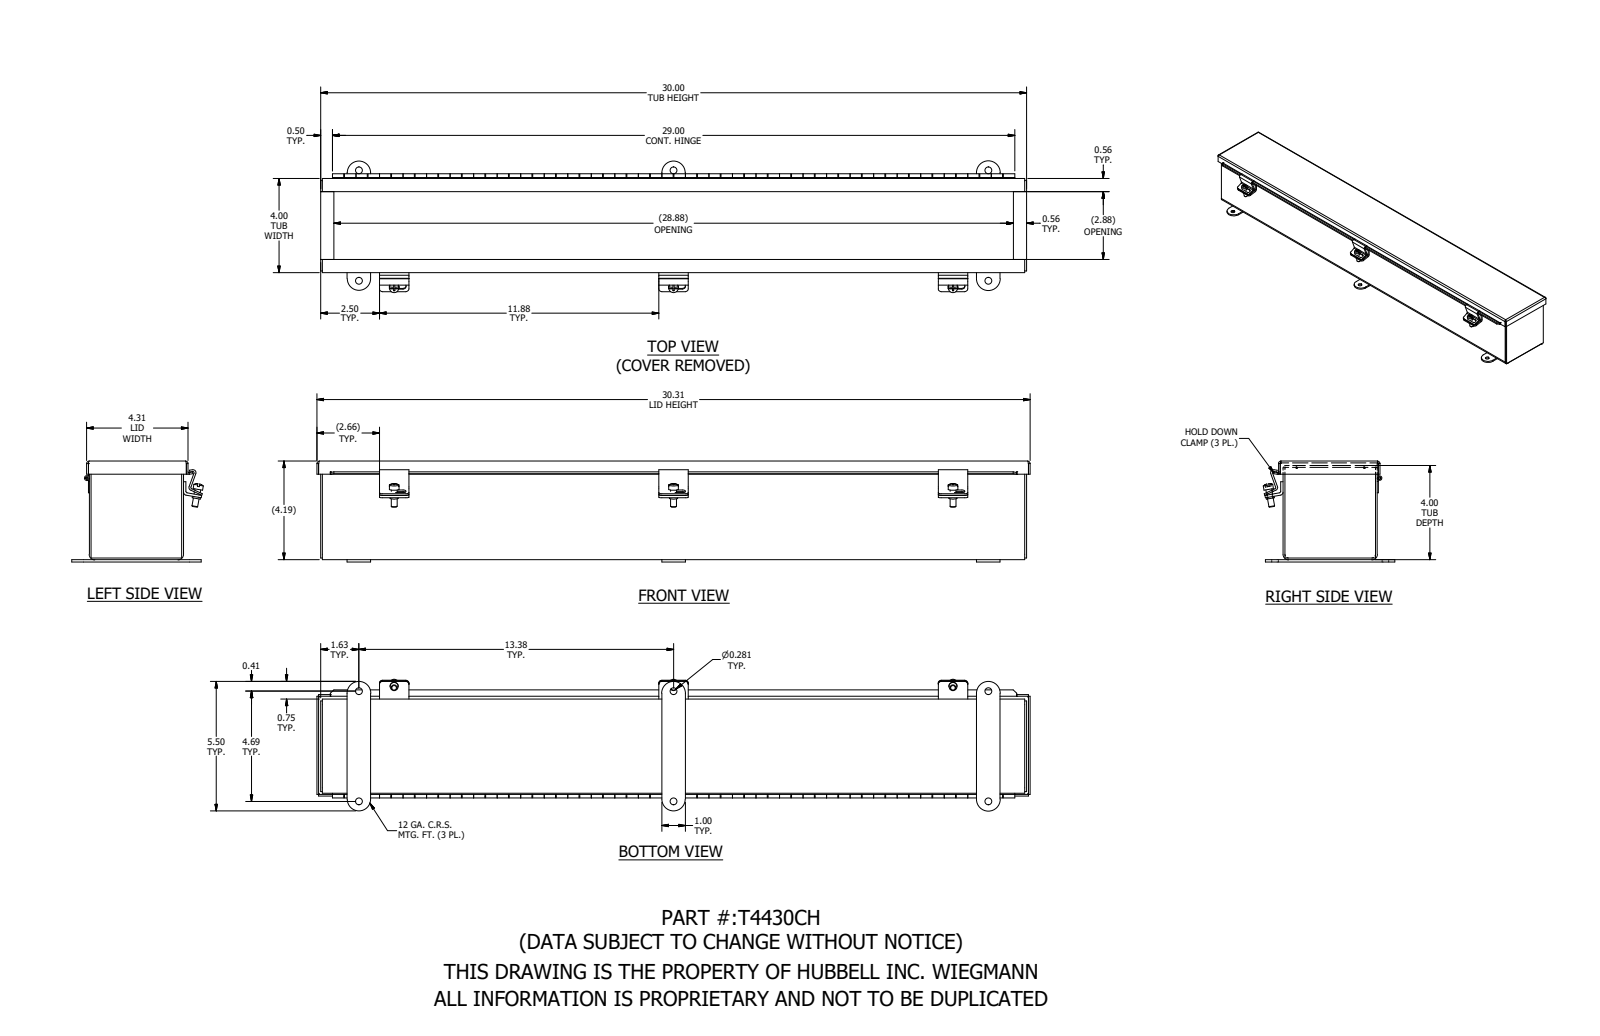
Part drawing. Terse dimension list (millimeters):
name: T4430CH
written by: SolidWorks 2021 (AUTOMOTIVE_DESIGN)
unit: mm
bodies: 19 solids, 741 faces (378 planar, 340 cylindrical, 23 other)
size: 770 × 142.1 × 108.8
volume: 773 500 mm³; area: 858 100 mm²
holes: 6× ⌀7.1, 3× ⌀5, 1× ⌀2.9
bosses: 3× ⌀10.4, 3× ⌀8.7, 3× ⌀6.4, 1× ⌀5.1, 1× ⌀2.5
rounds: 12× R3.2, 9× R0.8, 9× R2.7, 6× R3.4, 6× R12.7, 3× R1.6, 3× R3.2, 2× R4
face distances: 1.9, 99.7, 104.5, 101.6, 97.8, 106.4, 102.6, 4.8, 102.7, 2.9
hole spacings: 119, 339.7, 339.7, 360, 360, 679.5, 689.8, 301.6
